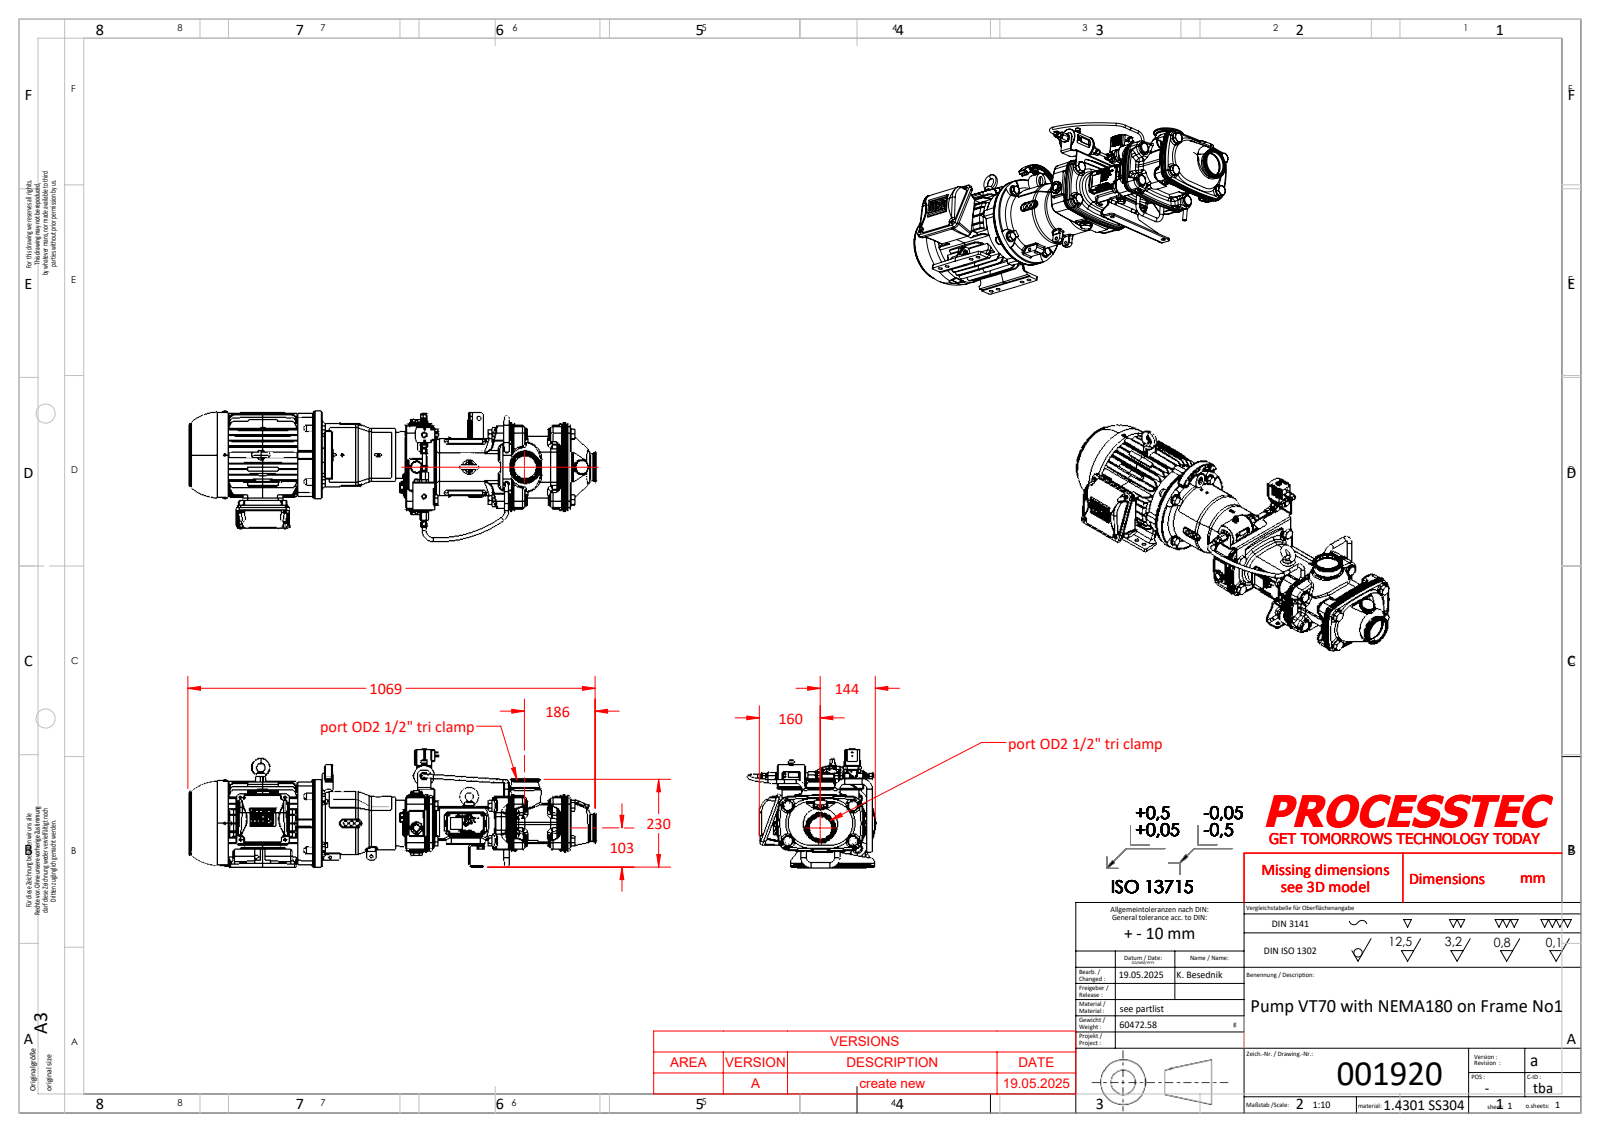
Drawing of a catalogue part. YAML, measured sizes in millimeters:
part_name: "001104_ISO 10642 - M6 x 16 - 16N; 000824; 001377; 001187_Washer ISO 7089 - 10 (+8 more)"
step_written_by: "SolidWorks 2023 (AUTOMOTIVE_DESIGN)"
units: millimeters
bodies: {solids: 88, faces: 11140, planar: 5694, cylindrical: 1531, other: 3915}
overall_size: [1068.7, 337.38, 308.97]
volume: 23390000
surface_area: 2158000
round_holes:
  - {diameter: 8, count: 17}
  - {diameter: 14, count: 10}
  - {diameter: 8.5, count: 9}
  - {diameter: 10.41, count: 8}
  - {diameter: 12, count: 7}
  - {diameter: 2.5, count: 5}
  - {diameter: 4, count: 5}
  - {diameter: 17.5, count: 5}
  - {diameter: 3.4, count: 4}
  - {diameter: 10.72, count: 4}
  - {diameter: 12.7, count: 4}
  - {diameter: 13.49, count: 4}
round_bosses_or_shafts:
  - {diameter: 10, count: 13}
  - {diameter: 16, count: 10}
  - {diameter: 24, count: 8}
  - {diameter: 5, count: 6}
  - {diameter: 28, count: 5}
  - {diameter: 26.97, count: 4}
  - {diameter: 12.7, count: 4}
  - {diameter: 40, count: 3}
partial_cylinders:
  - {radius: 3, count: 82}
  - {radius: 2, count: 65}
  - {radius: 5, count: 38}
  - {radius: 8, count: 36}
  - {radius: 4, count: 22}
  - {radius: 6, count: 20}
  - {radius: 10, count: 18}
  - {radius: 1.4, count: 16}
face_to_face_distances: [14.5, 340.8, 522.9, 182.1, 359.8, 4.7, 882.7, 700.6, 87.5, 51.8]
hole_center_spacings: [83.08, 41, 45, 68.14, 22.59, 132.11, 71.02, 40.99]
